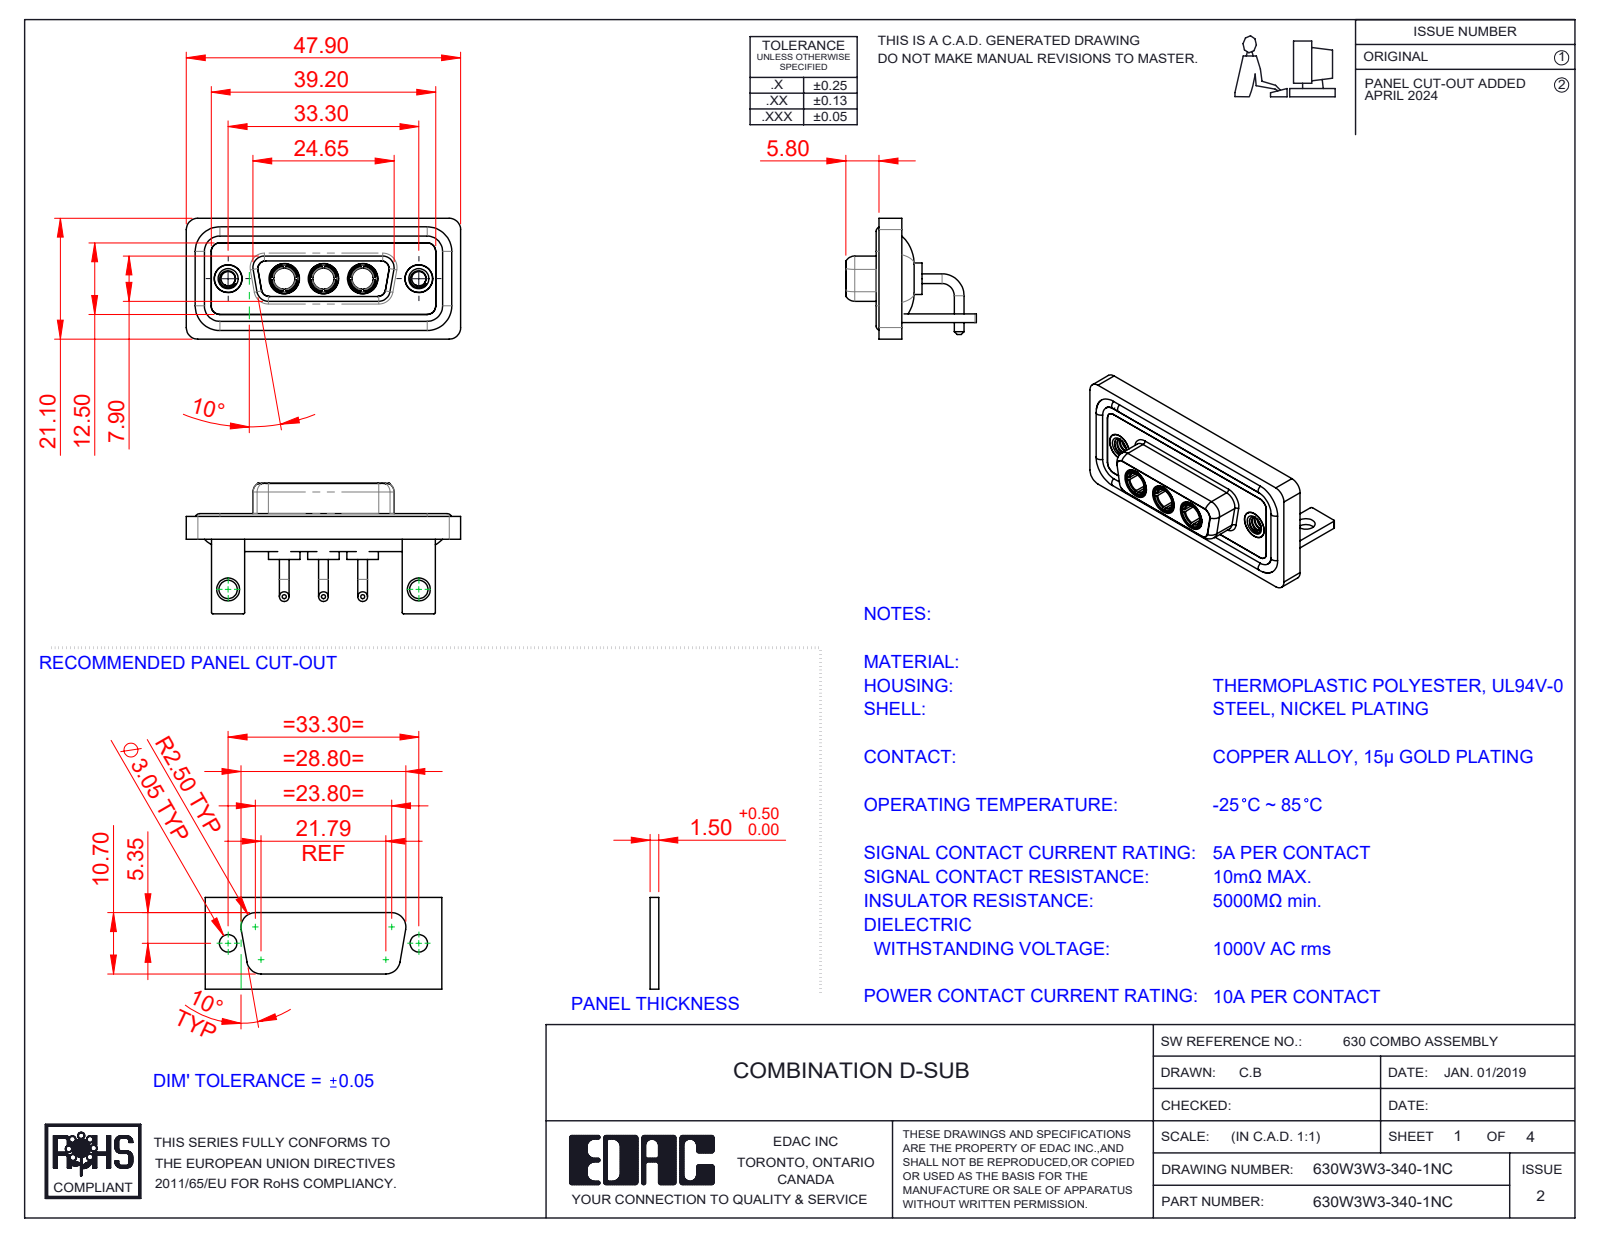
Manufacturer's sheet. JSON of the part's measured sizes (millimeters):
{"part_name": "Power Socket_10A RA; 630Combo Waterproof Housing_15 Contacts; 630Combo Shell Rear_15 Contacts; 630Combo Housing_3W3 (+4 more)", "step_written_by": "SolidWorks 2023 (CONFIG_CONTROL_DESIGN)", "units": "millimeters", "bodies": {"solids": 15, "faces": 662, "planar": 212, "cylindrical": 285, "other": 165}, "overall_size": [47.9, 22.8, 21.1], "volume_mm3": 6366, "surface_area_mm2": 10558, "round_holes": [[4.85, 5], [3.7, 3], [5.3, 3], [2.5, 2], [3.2, 2], [4, 2], [4.05, 2], [5, 2]], "round_bosses_or_shafts": [[1.7, 6], [1.6, 4], [5.5, 3], [5.2, 3], [4.96, 3], [4.75, 3], [3.75, 3], [4.95, 2]], "partial_cylinders_radius": [[2, 21], [1.5, 18], [0.25, 16], [1.35, 12], [1.6, 8], [0.5, 5], [0.6, 4], [0.65, 4]], "face_to_face_distances": [0.4, 2.9, 1.5, 1.8, 3.7, 1.1, 4.1, 1.6, 2.5, 1.4], "hole_center_spacings": [6.85, 9.8, 16.65, 23.5, 33.3, 13.7]}
